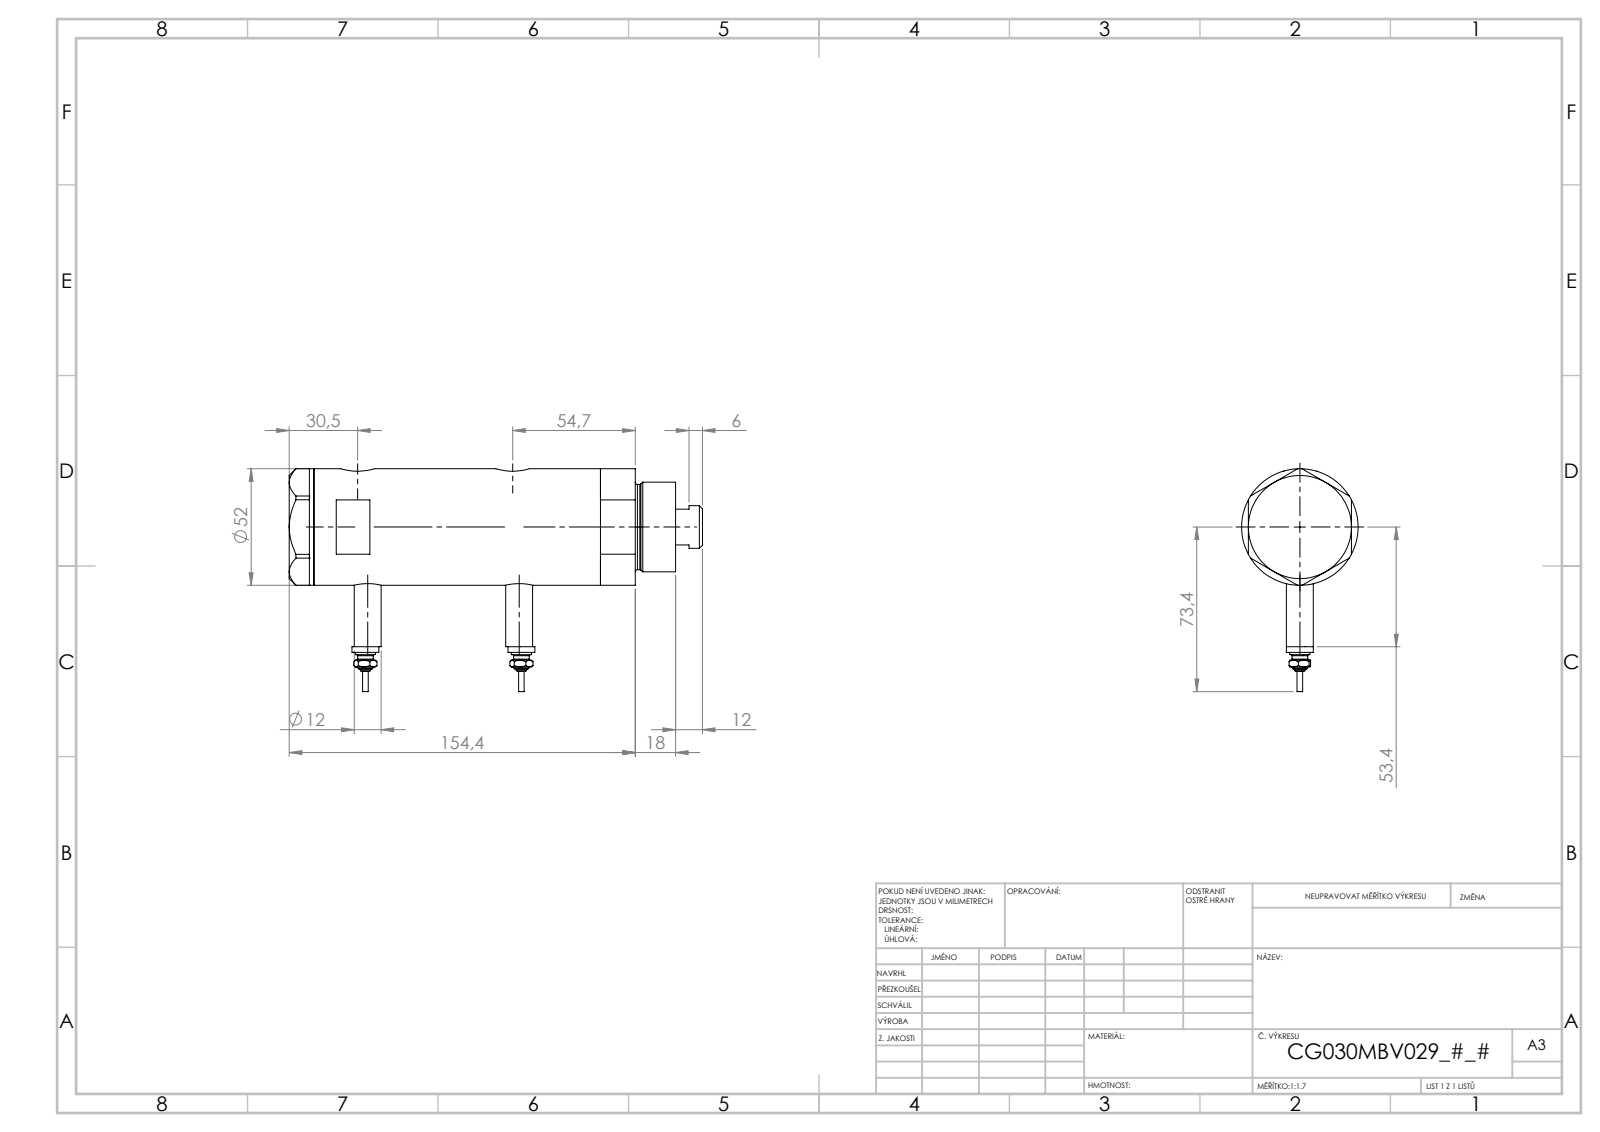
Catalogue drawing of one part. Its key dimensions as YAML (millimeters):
part_name: "Switch; V270CG_BACK; V270CG_FRONT; V270CG_VC (+1 more)"
step_written_by: "SolidWorks 2019 (CONFIG_CONTROL_DESIGN)"
units: millimeters
bodies: {solids: 6, faces: 226, planar: 93, cylindrical: 69, other: 64}
overall_size: [184.4, 99.4, 52]
volume: 341327
surface_area: 79945
round_holes:
  - {diameter: 9.73, count: 2}
  - {diameter: 12.5, count: 2}
  - {diameter: 15, count: 2}
  - {diameter: 6.5, count: 1}
  - {diameter: 20, count: 1}
  - {diameter: 21.5, count: 1}
  - {diameter: 30, count: 1}
  - {diameter: 33, count: 1}
  - {diameter: 44, count: 1}
round_bosses_or_shafts:
  - {diameter: 12, count: 4}
  - {diameter: 9, count: 2}
  - {diameter: 7, count: 2}
  - {diameter: 4.5, count: 2}
  - {diameter: 2.5, count: 2}
  - {diameter: 52, count: 1}
  - {diameter: 40, count: 1}
  - {diameter: 38, count: 1}
face_to_face_distances: [91.5, 23.8, 67.7, 11, 34.8, 102.5, 46, 36.4, 138.9, 127.9]
hole_center_spacings: [2.9, 4.5, 64.7, 67.6, 69.2, 72.1]
